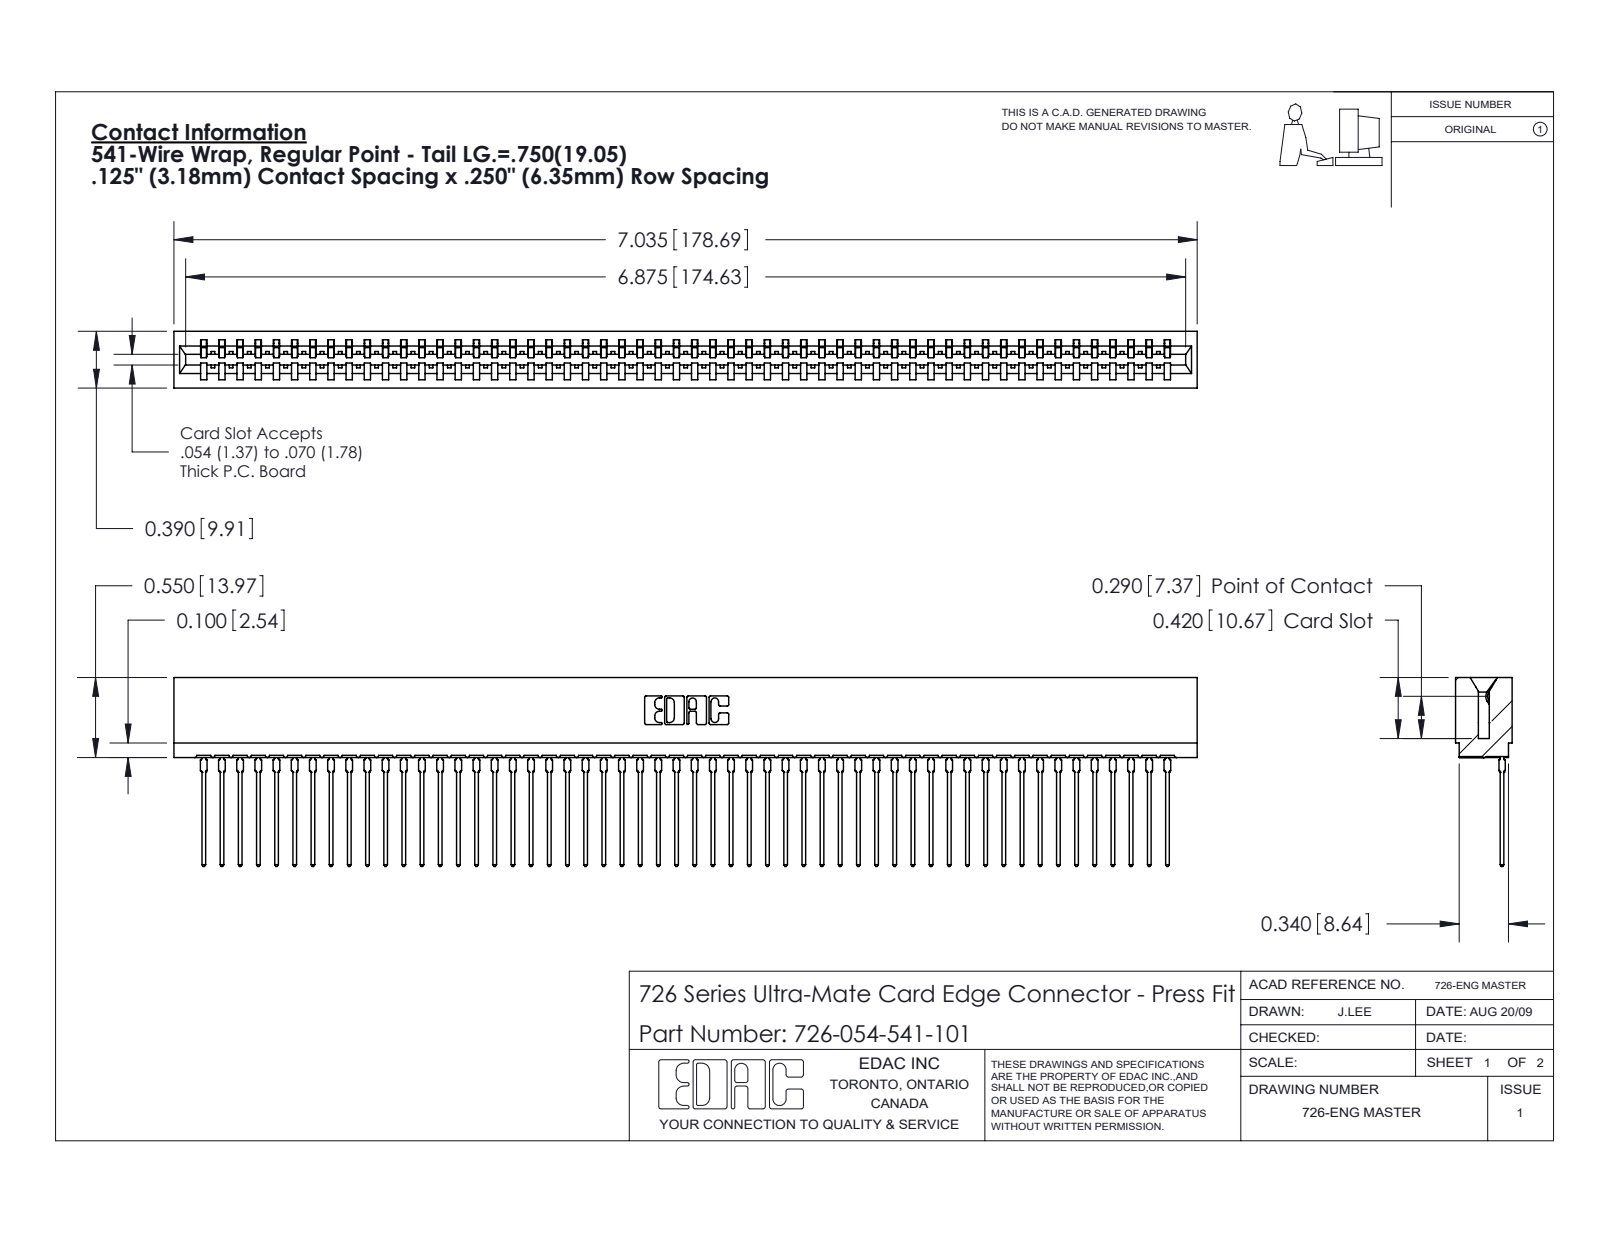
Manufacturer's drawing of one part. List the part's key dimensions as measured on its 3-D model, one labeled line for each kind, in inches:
Part name (STEP PRODUCT): 726 Part_.515 Slot Depth - 01; 746-292-001_541; 726-054-541-101
STEP written by: SolidWorks 2020 (CONFIG_CONTROL_DESIGN)
Units: inches
Bodies: 55 solids, 5929 faces (3457 planar, 1068 cylindrical, 1404 other)
Overall size (bounding box): 7.035 × 1.299 × 0.39
Volume: 0.985 in³ · Surface area: 40.46 in²
Partial cylindrical surfaces — rounded edges, fillets, slot ends (radius × count): R0.021 ×108, R0.015 ×55, R0.01 ×22, R0.007 ×6, R0.031 ×6, R0.005 ×4, R0.011 ×4, R0.026 ×3
Main face-to-face distances: 0.057, 0.333, 0.39, 0.025, 0.307, 0.25, 0.083, 0.275, 0.365, 0.032
